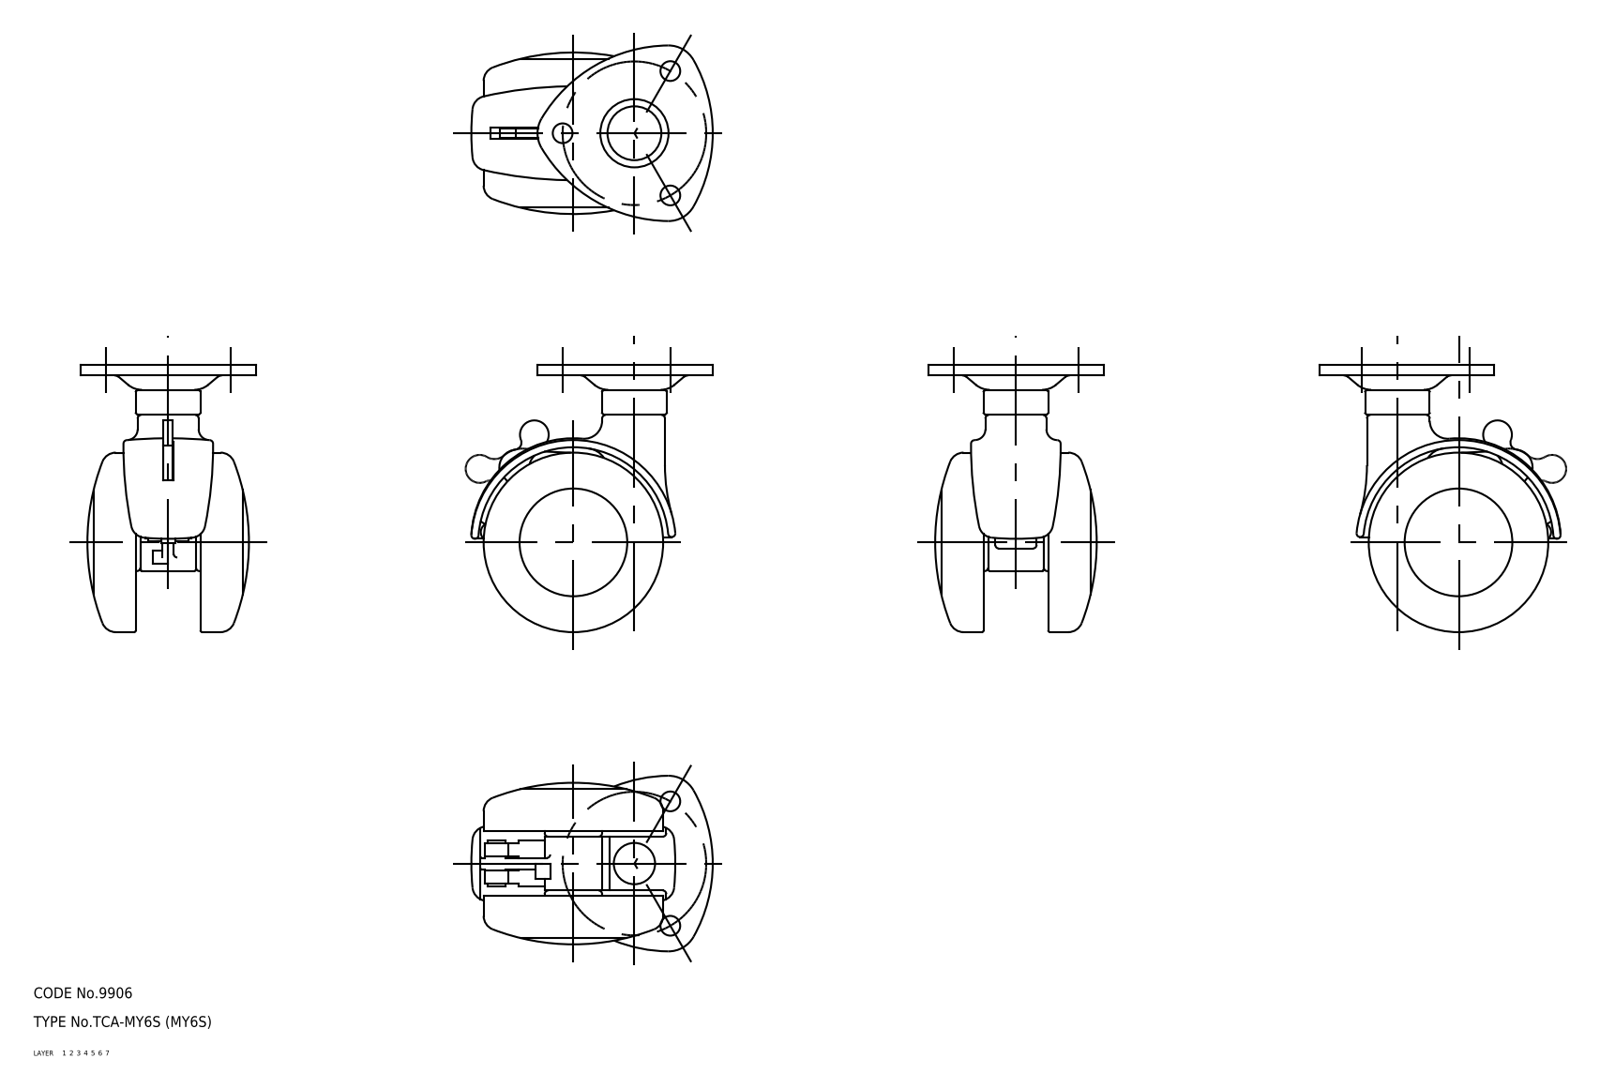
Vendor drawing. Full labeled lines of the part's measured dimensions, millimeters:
Part name (STEP PRODUCT): wheel; mounting plate; main shaft; lever (+1 more)
STEP written by: CADfix (AUTOMOTIVE_DESIGN)
Units: millimetres
Bodies: 7 solids, 221 faces (0 planar, 0 cylindrical, 221 other)
Overall size (bounding box): 74.5 × 68.82 × 48.91
Volume: 60 484 mm³ · Surface area: 33 080 mm²
